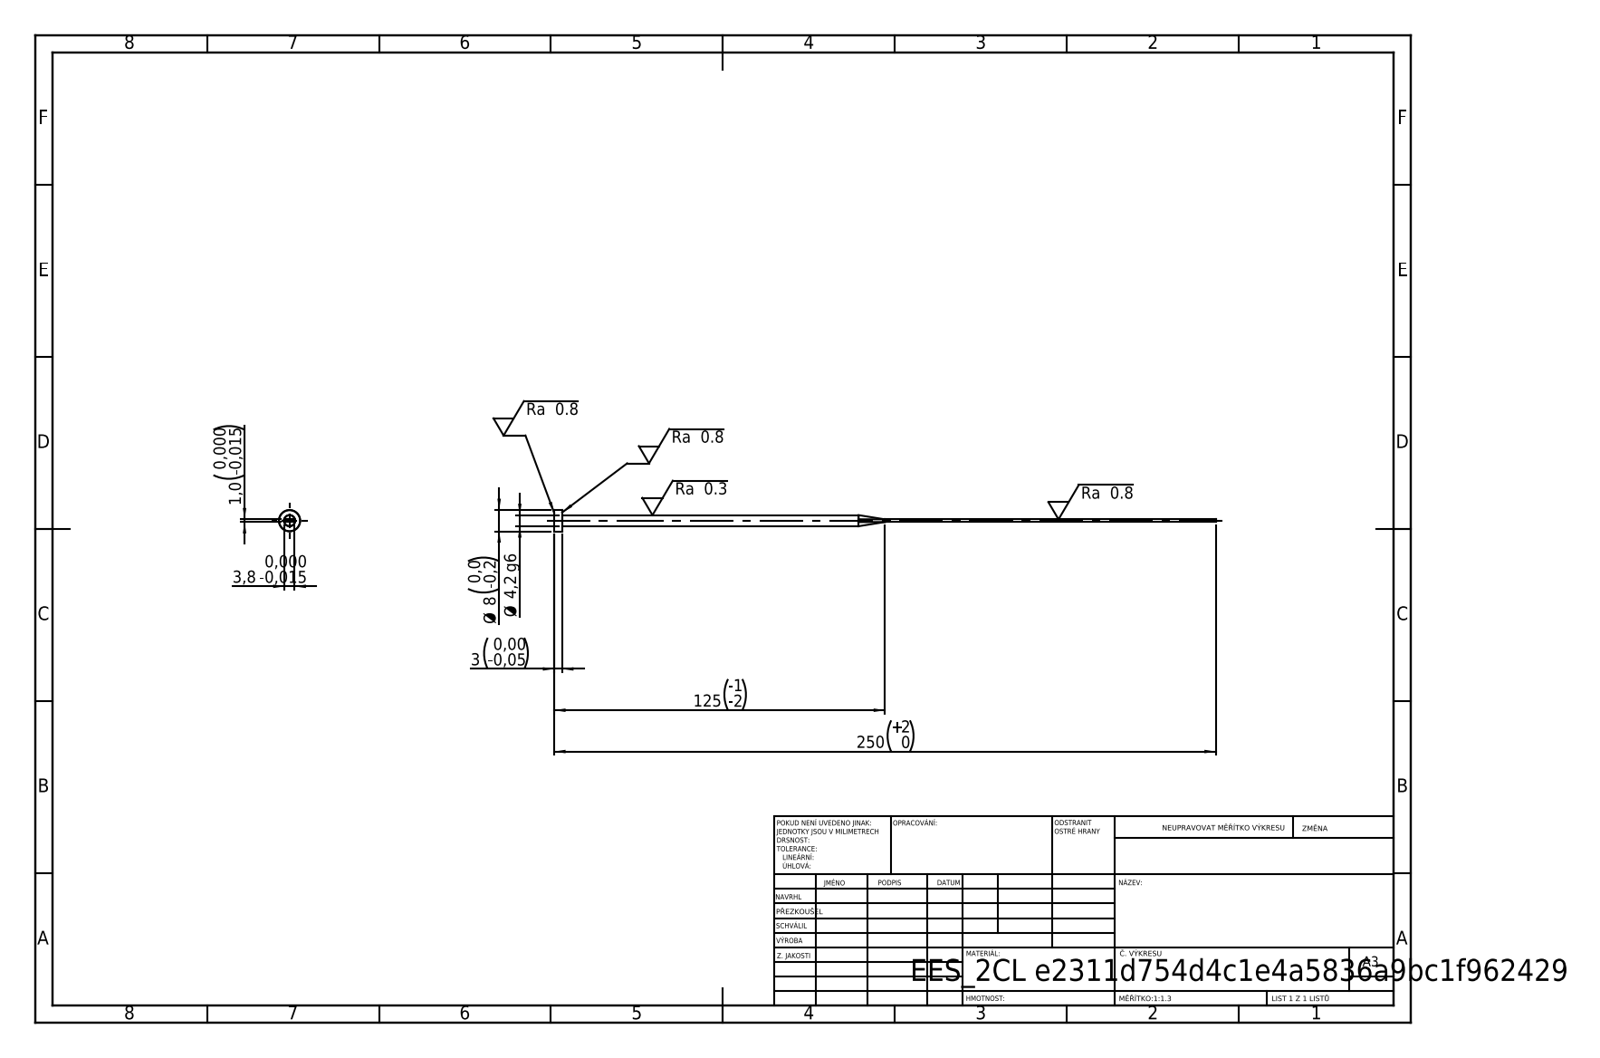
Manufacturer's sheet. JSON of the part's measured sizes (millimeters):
{"step_written_by": "SolidWorks 2019 (CONFIG_CONTROL_DESIGN)", "units": "millimeters", "bodies": {"solids": 1, "faces": 15, "planar": 7, "cylindrical": 4, "other": 4}, "overall_size": [250, 8, 8], "volume_mm3": 2262, "surface_area_mm2": 2954, "round_bosses_or_shafts": [[8, 1], [4.2, 1]], "face_to_face_distances": [1, 3.8, 3, 250, 247]}
